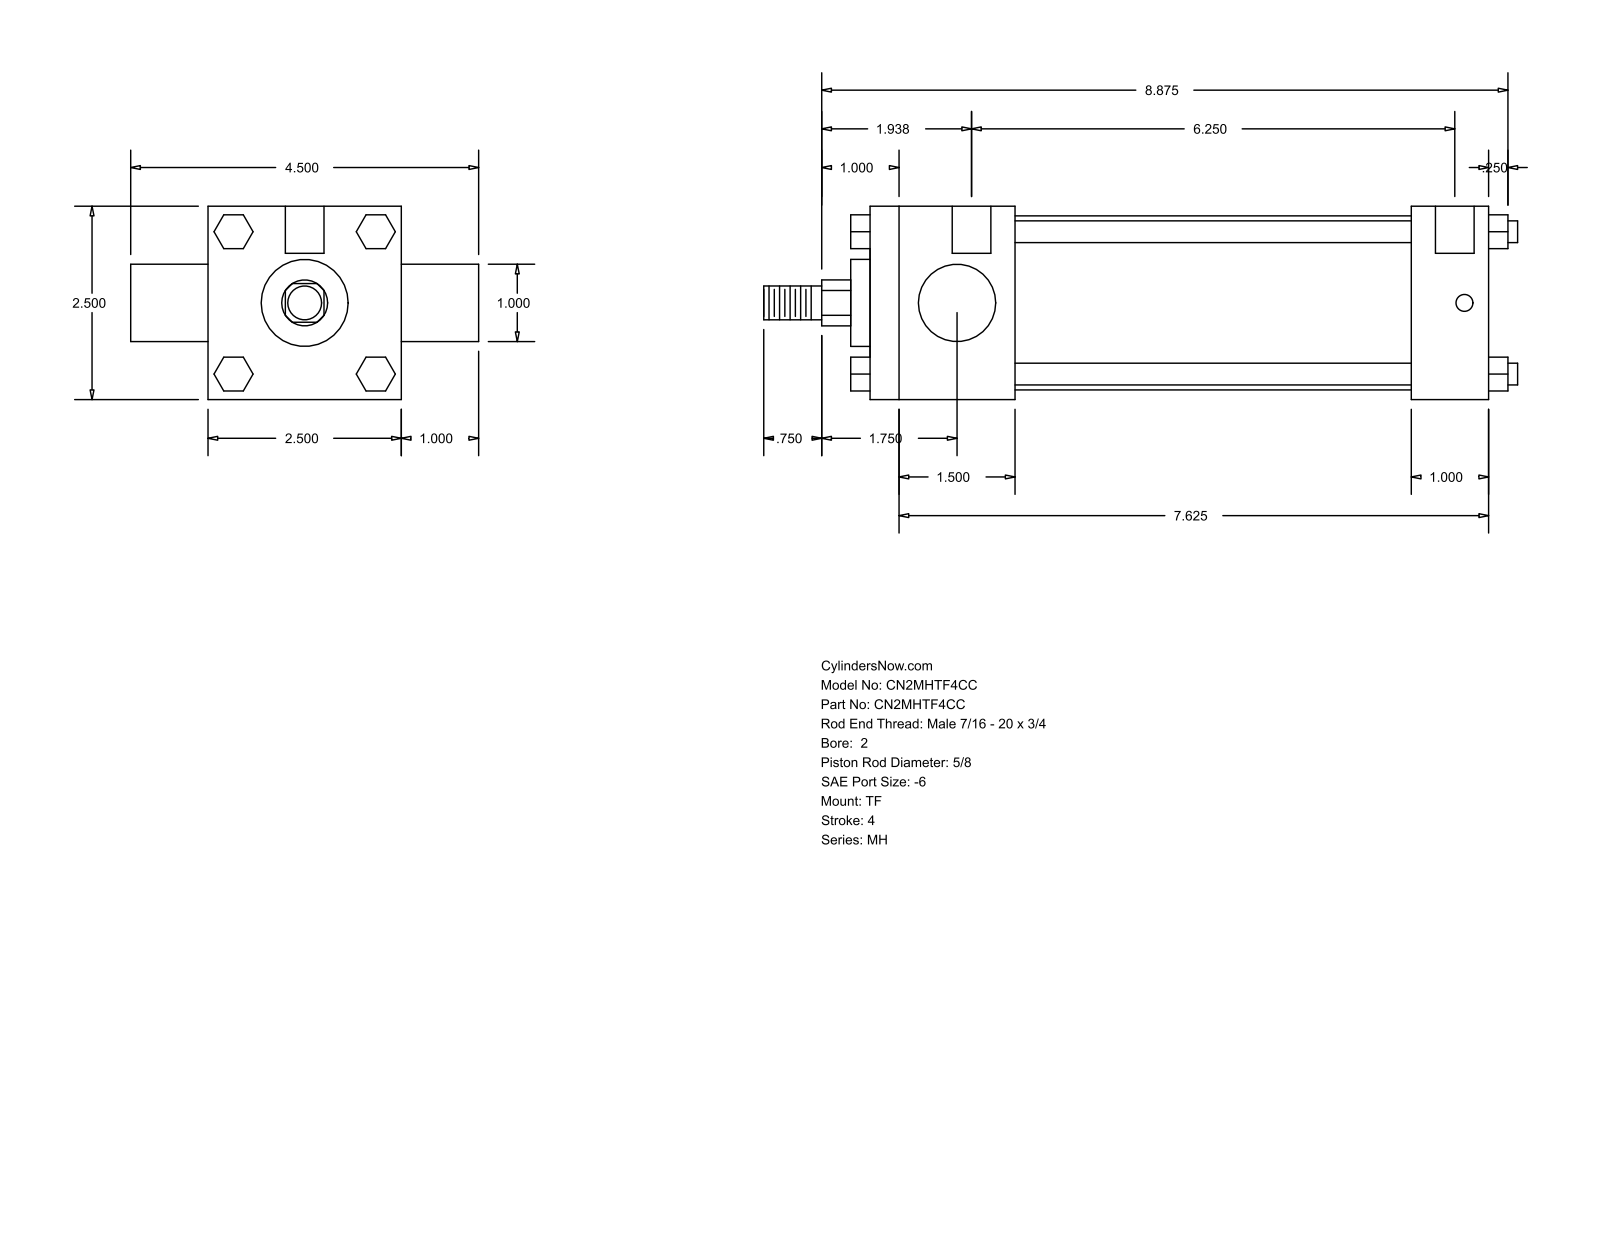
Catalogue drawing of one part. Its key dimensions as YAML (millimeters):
part_name: "MH_TF__0200_0.625"
step_written_by: "GSSL Pune (CONFIG_CONTROL_DESIGN)"
units: millimeters
bodies: {solids: 0, faces: 120, planar: 92, cylindrical: 28, other: 0}
overall_size: [247.65, 114.3, 63.5]
round_holes:
  - {diameter: 5.56, count: 3}
  - {diameter: 12.7, count: 2}
round_bosses_or_shafts:
  - {diameter: 7.14, count: 4}
  - {diameter: 57.15, count: 1}
  - {diameter: 28.57, count: 1}
  - {diameter: 25.4, count: 1}
  - {diameter: 15.88, count: 1}
  - {diameter: 11.11, count: 1}
partial_cylinders:
  - {radius: 7.54, count: 1}
face_to_face_distances: [63.5, 203.19, 47.62, 177.8, 130.18, 155.57, 25.39, 25.4, 88.9, 6.35]
hole_center_spacings: [3.18, 4.76, 158.75, 161.93, 163.51, 166.69]
